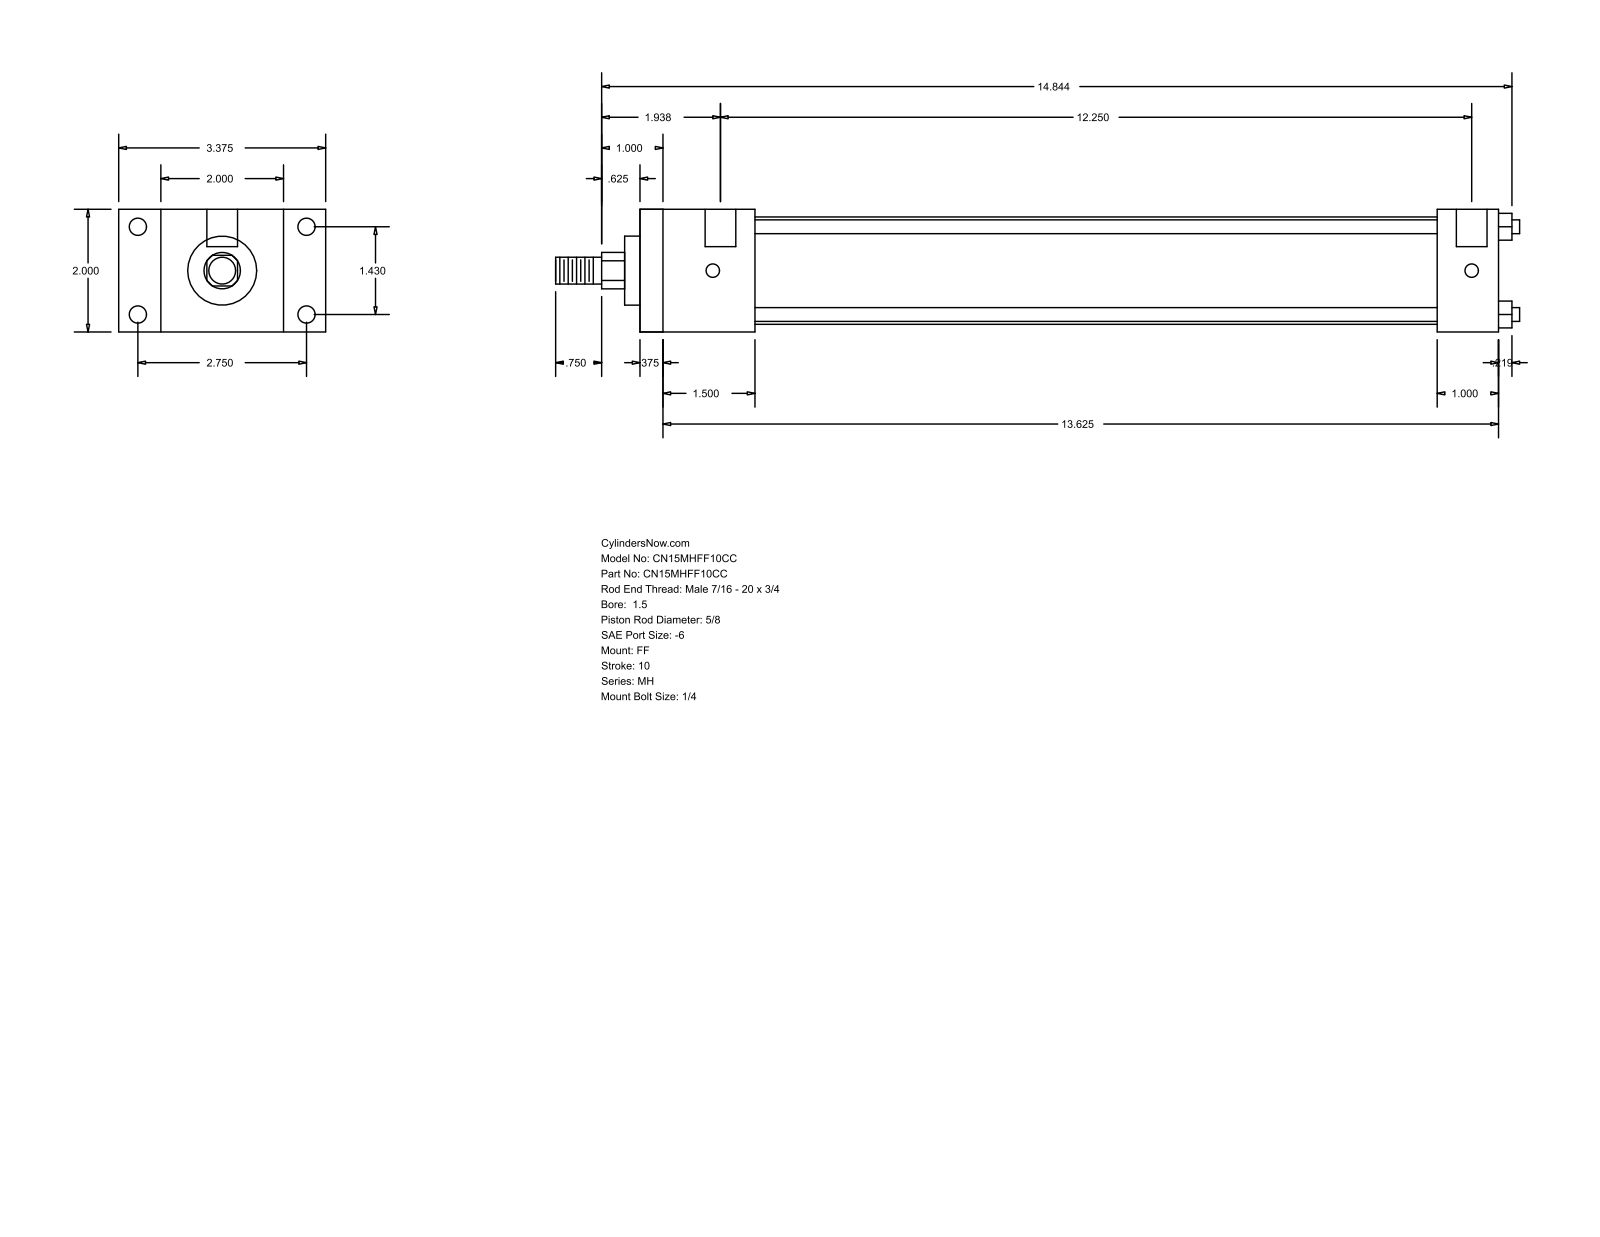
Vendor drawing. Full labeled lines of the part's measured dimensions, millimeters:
Part name (STEP PRODUCT): MH_FF__0150_0.625
STEP written by: GSSL Pune (CONFIG_CONTROL_DESIGN)
Units: millimetres
Bodies: 0 solids, 92 faces (64 planar, 28 cylindrical, 0 other)
Overall size (bounding box): 399.26 × 85.72 × 50.8
Round holes (diameter × count): ⌀5.56 ×4, ⌀7.14 ×4, ⌀12.7 ×2
Round bosses / shafts (diameter × count): ⌀5.71 ×4, ⌀44.45 ×1, ⌀28.57 ×1, ⌀15.88 ×1, ⌀11.11 ×1
Partial cylindrical surfaces — rounded edges, fillets, slot ends (radius × count): R7.54 ×1
Main face-to-face distances: 50.8, 355.6, 9.52, 346.08, 17.46, 68.26, 47.62, 38.1, 307.98, 330.19
Hole centre spacings: 36.32, 69.84, 78.72, 314.32, 3.17, 311.15
